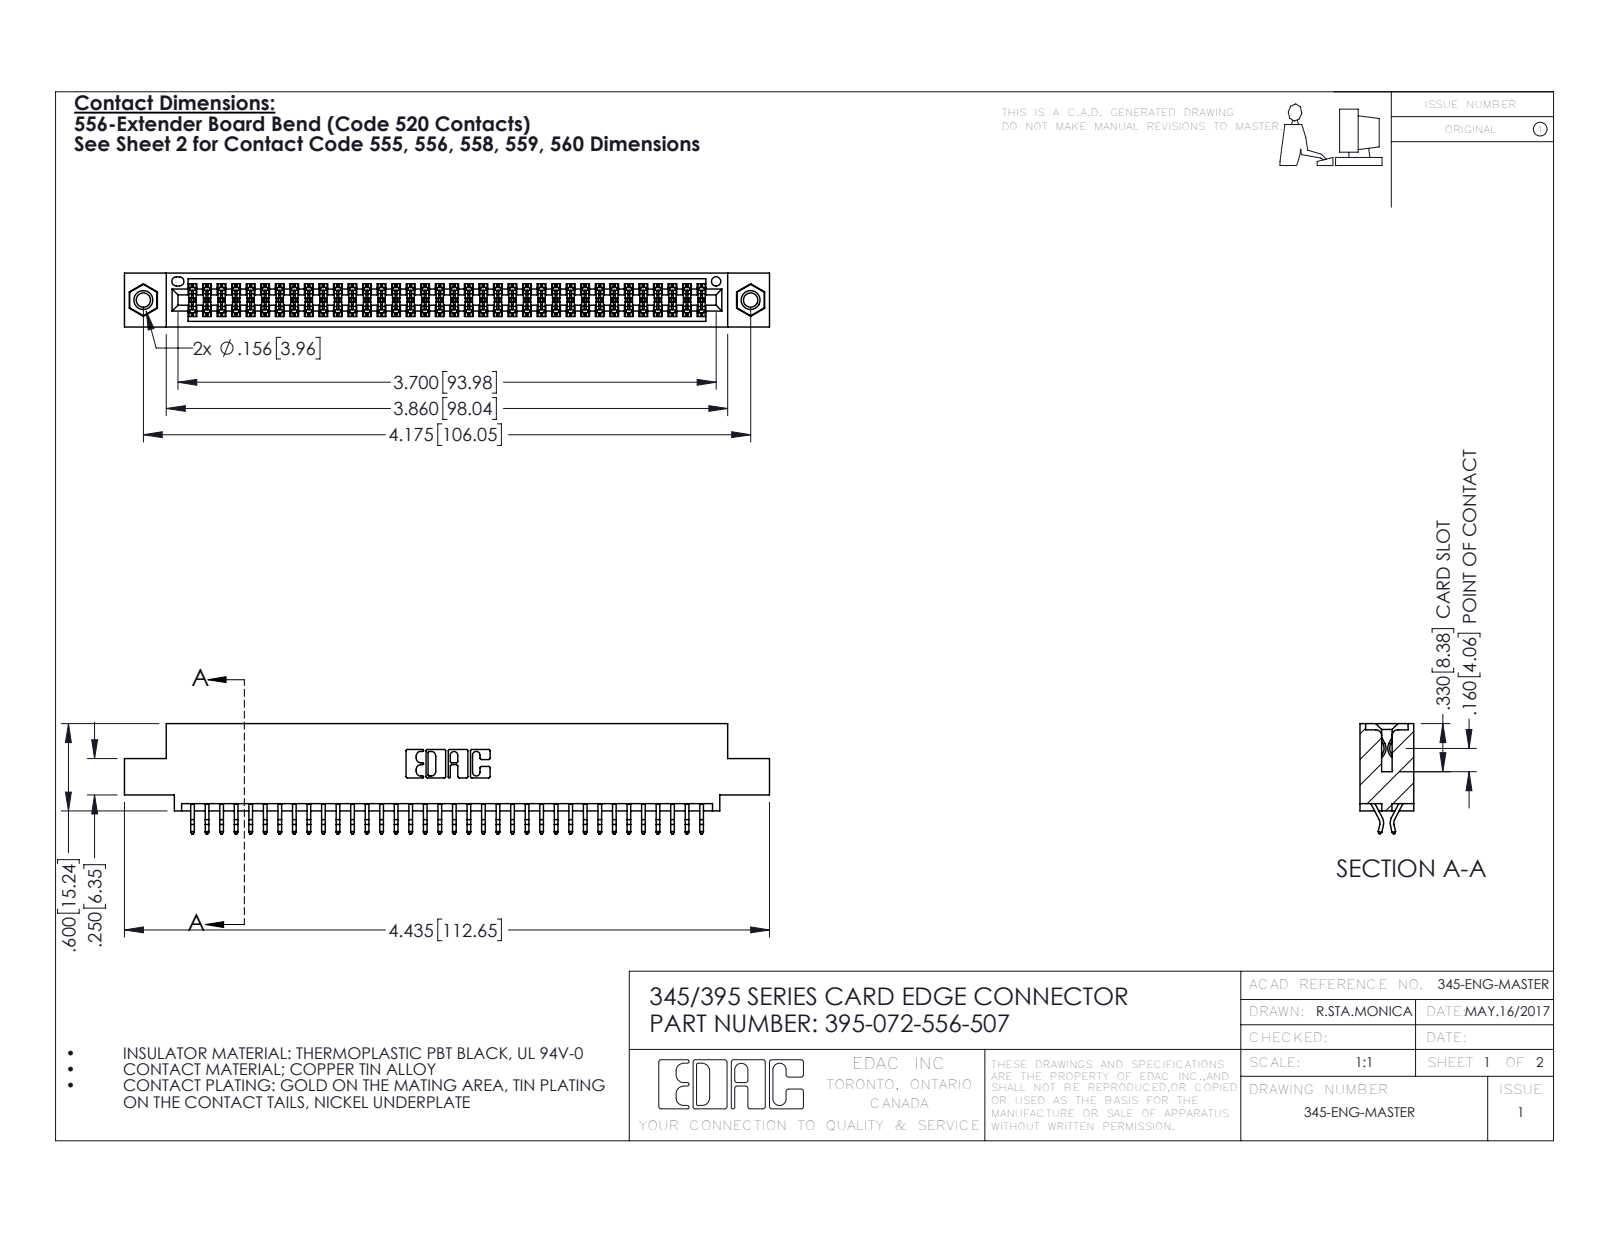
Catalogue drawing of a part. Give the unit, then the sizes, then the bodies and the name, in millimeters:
Units: millimetres
Overall size (bounding box): 112.6 × 19.2 × 9.4
Round holes (diameter × count): ⌀2.5 ×2, ⌀3.2 ×2, ⌀4 ×2, ⌀1.6 ×1
Round bosses / shafts (diameter × count): ⌀3.9 ×2
Partial cylindrical surfaces — rounded edges, fillets, slot ends (radius × count): R0.2 ×108, R0.3 ×22, R0.2 ×6, R0.8 ×6, R0.7 ×3, R0.3 ×2, R0.4 ×2, R0.5 ×2
Main face-to-face distances: 1.8, 7.6, 9.4, 5.1, 0.6, 2.5, 6.9, 5.7, 4.4, 3.8
Hole centre spacings: 6.9, 100.1, 106
Volume: 10 800 mm³ · Surface area: 15 900 mm²
Bodies: 75 solids, 4222 faces (2780 planar, 1426 cylindrical, 16 other)
Part name (STEP PRODUCT): 345 Part_0.110 Offset - 0.156 Dia-TI; 395-072-556-507; 345-250-001_345-250-005-103; 345-292-001_556 Tail
STEP written by: SolidWorks 2016 (CONFIG_CONTROL_DESIGN)
